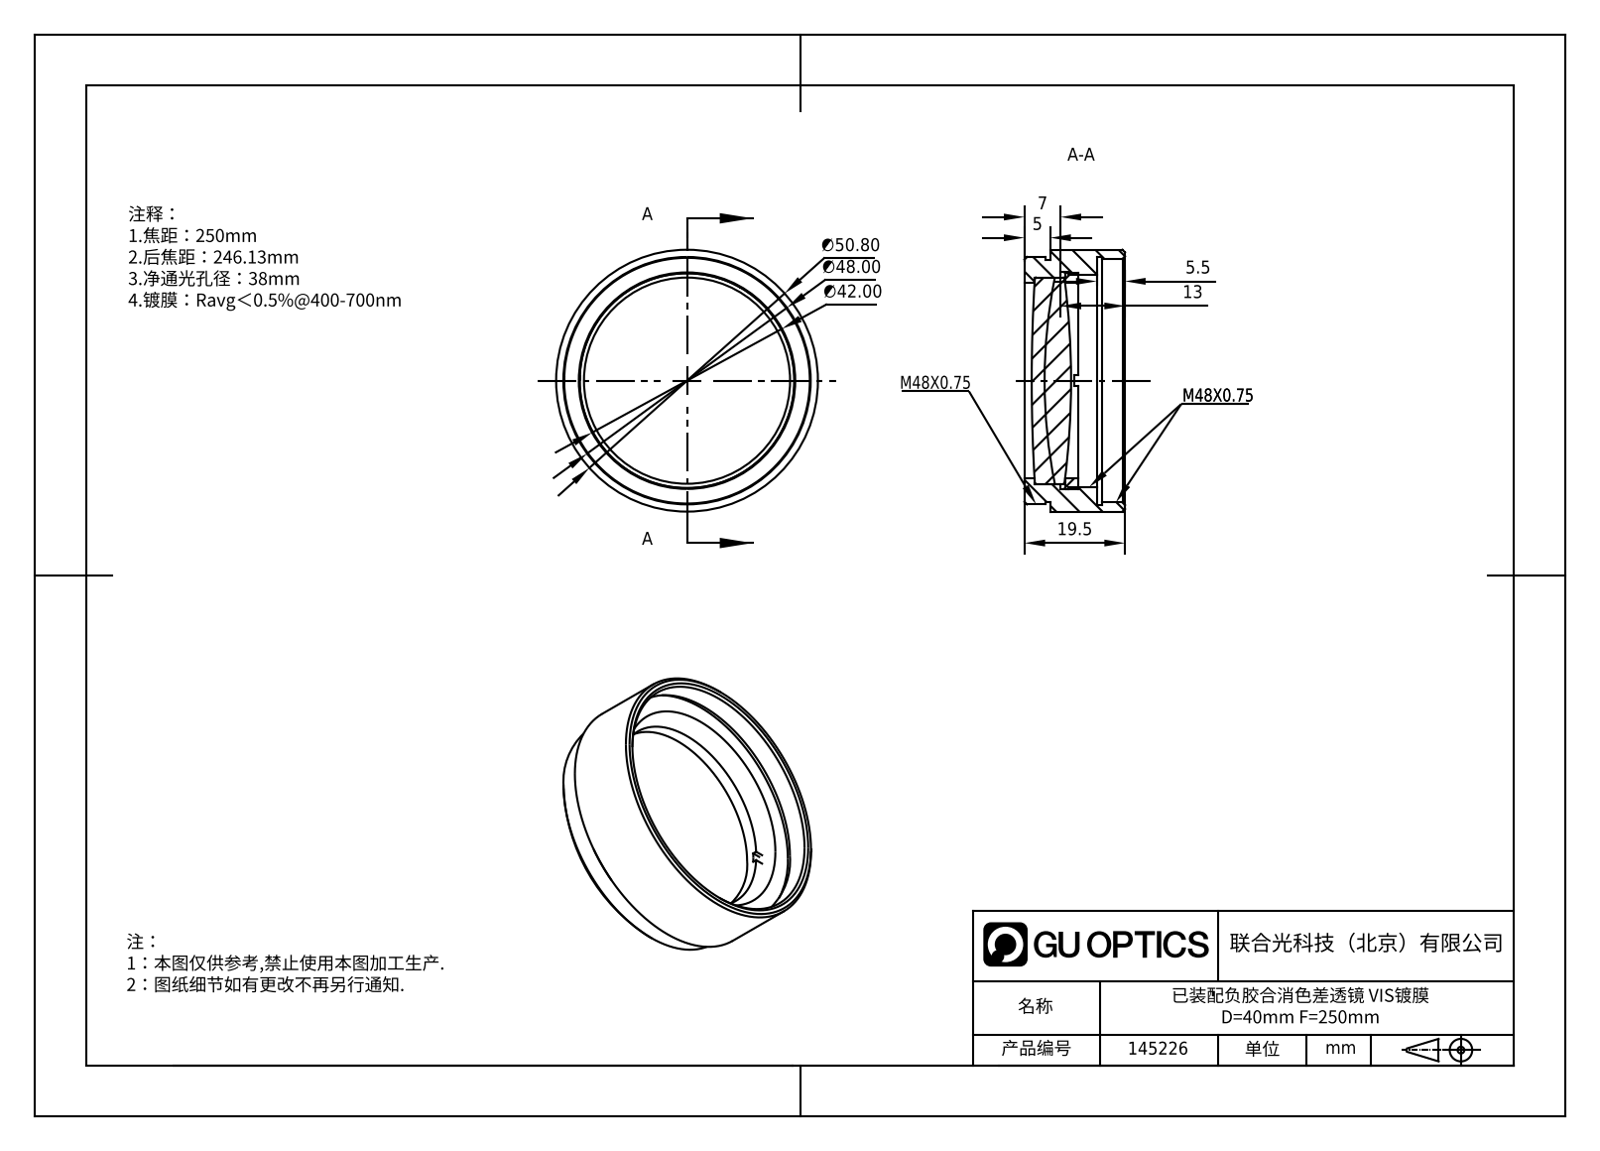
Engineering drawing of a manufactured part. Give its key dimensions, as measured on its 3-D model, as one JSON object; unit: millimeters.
{"part_name": "M42x0.75安装环PN35008-LM400-D1; GL31-040-250-VIS_Solidworks; M42x0.75ѹȦ; APD-ML40-250-VIS-A", "step_written_by": "SolidWorks 2022 (AUTOMOTIVE_DESIGN)", "units": "millimeters", "bodies": {"solids": 4, "faces": 64, "planar": 18, "cylindrical": 26, "other": 20}, "overall_size": [50.8, 50.8, 19.5], "volume_mm3": 19624, "surface_area_mm2": 14570, "round_holes": [[38, 1], [41.25, 1], [42.1, 1], [47.25, 1], [48.1, 1]], "round_bosses_or_shafts": [[50.8, 1], [48, 1], [47, 1], [42, 1], [40, 1]], "face_to_face_distances": [14, 5, 2, 9, 7, 10.37, 5.37, 3.63, 7.87, 2.87]}
